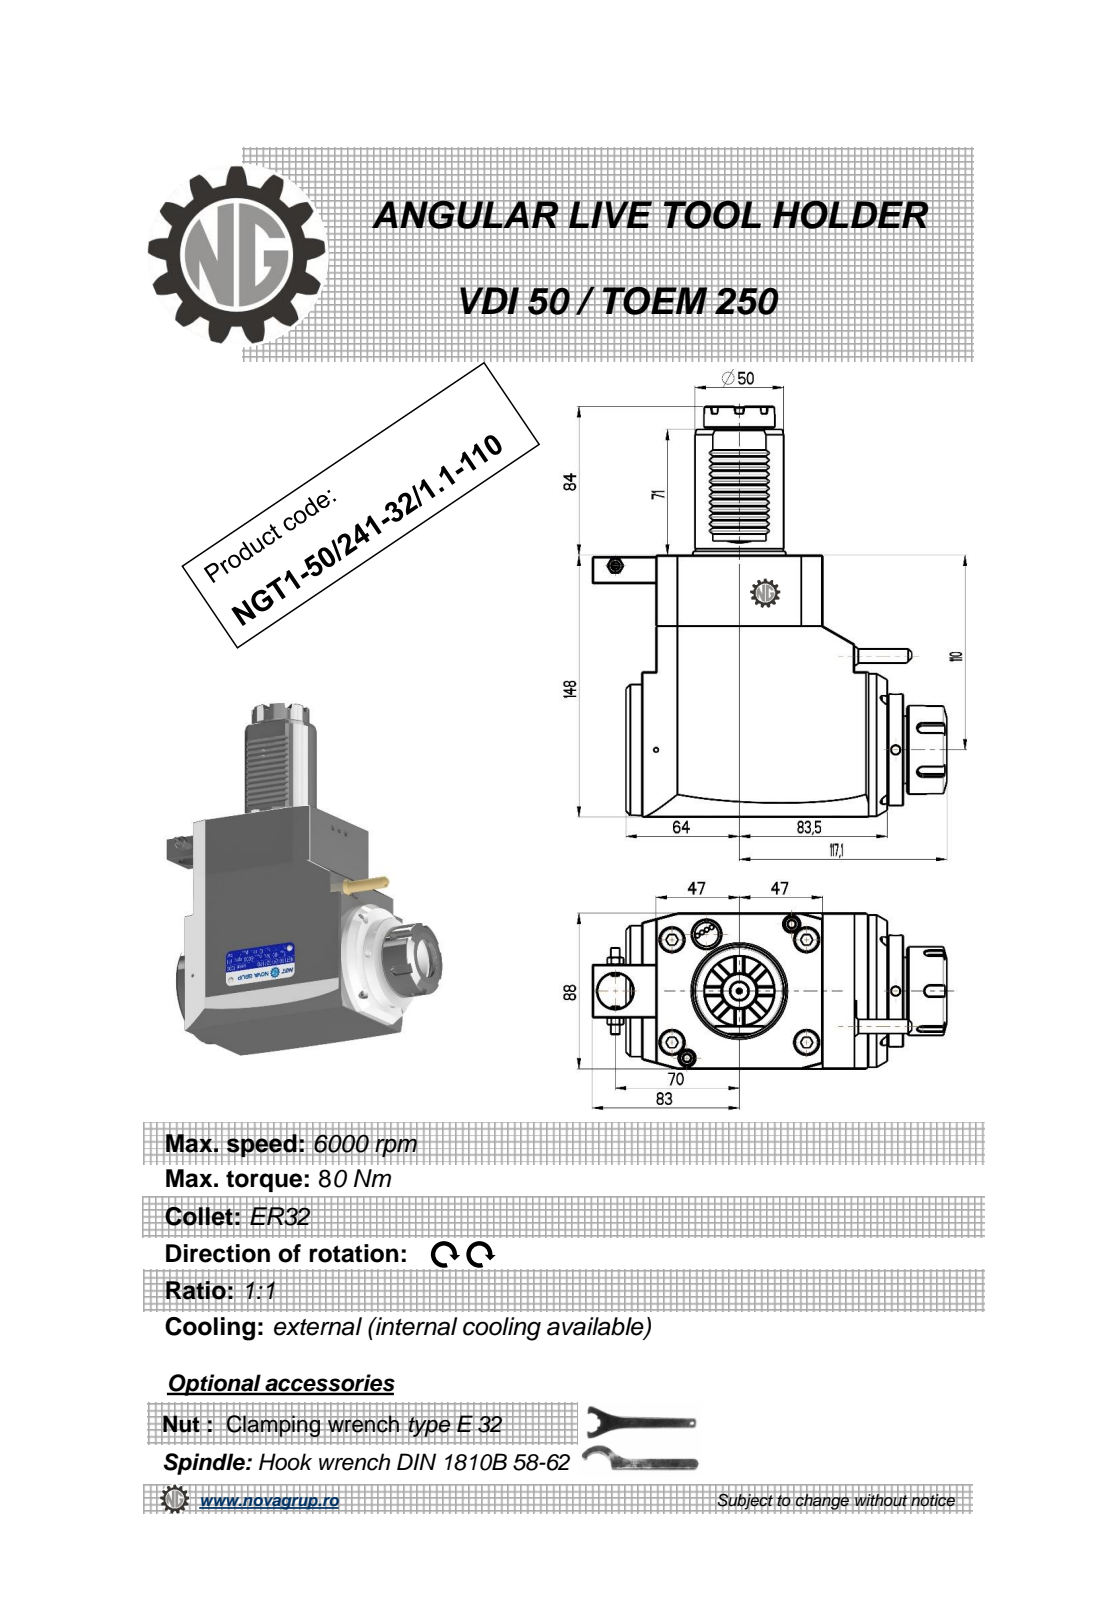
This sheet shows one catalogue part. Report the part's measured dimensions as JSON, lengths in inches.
{"part_name": "NGT1_50_241_32_1_1_110", "step_written_by": "PRO/ENGINEER BY PARAMETRIC TECHNOLOGY CORPORATION, 2010280 (CONFIG_CONTROL_DESIGN)", "units": "inches", "bodies": {"solids": 1, "faces": 473, "planar": 232, "cylindrical": 86, "other": 155}, "overall_size": [9.134, 7.878, 3.465], "volume_in3": 110.3, "surface_area_in2": 176.4, "round_holes": [[0.197, 3], [0.118, 1], [0.374, 1], [0.787, 1], [1.063, 1]], "round_bosses_or_shafts": [[1.969, 2], [3.386, 1], [2.913, 1], [2.48, 1], [1.988, 1], [1.614, 1], [1.575, 1], [0.807, 1]], "partial_cylinders_radius": [[0.01, 12], [0.012, 12], [0.008, 6], [0.118, 5]], "face_to_face_distances": [3.465, 5.827, 5.807, 0.354, 0.669, 0.315, 4.37, 3.701, 5.138, 1.437], "hole_center_spacings": [2.065, 2.23, 3.996, 6.23]}
